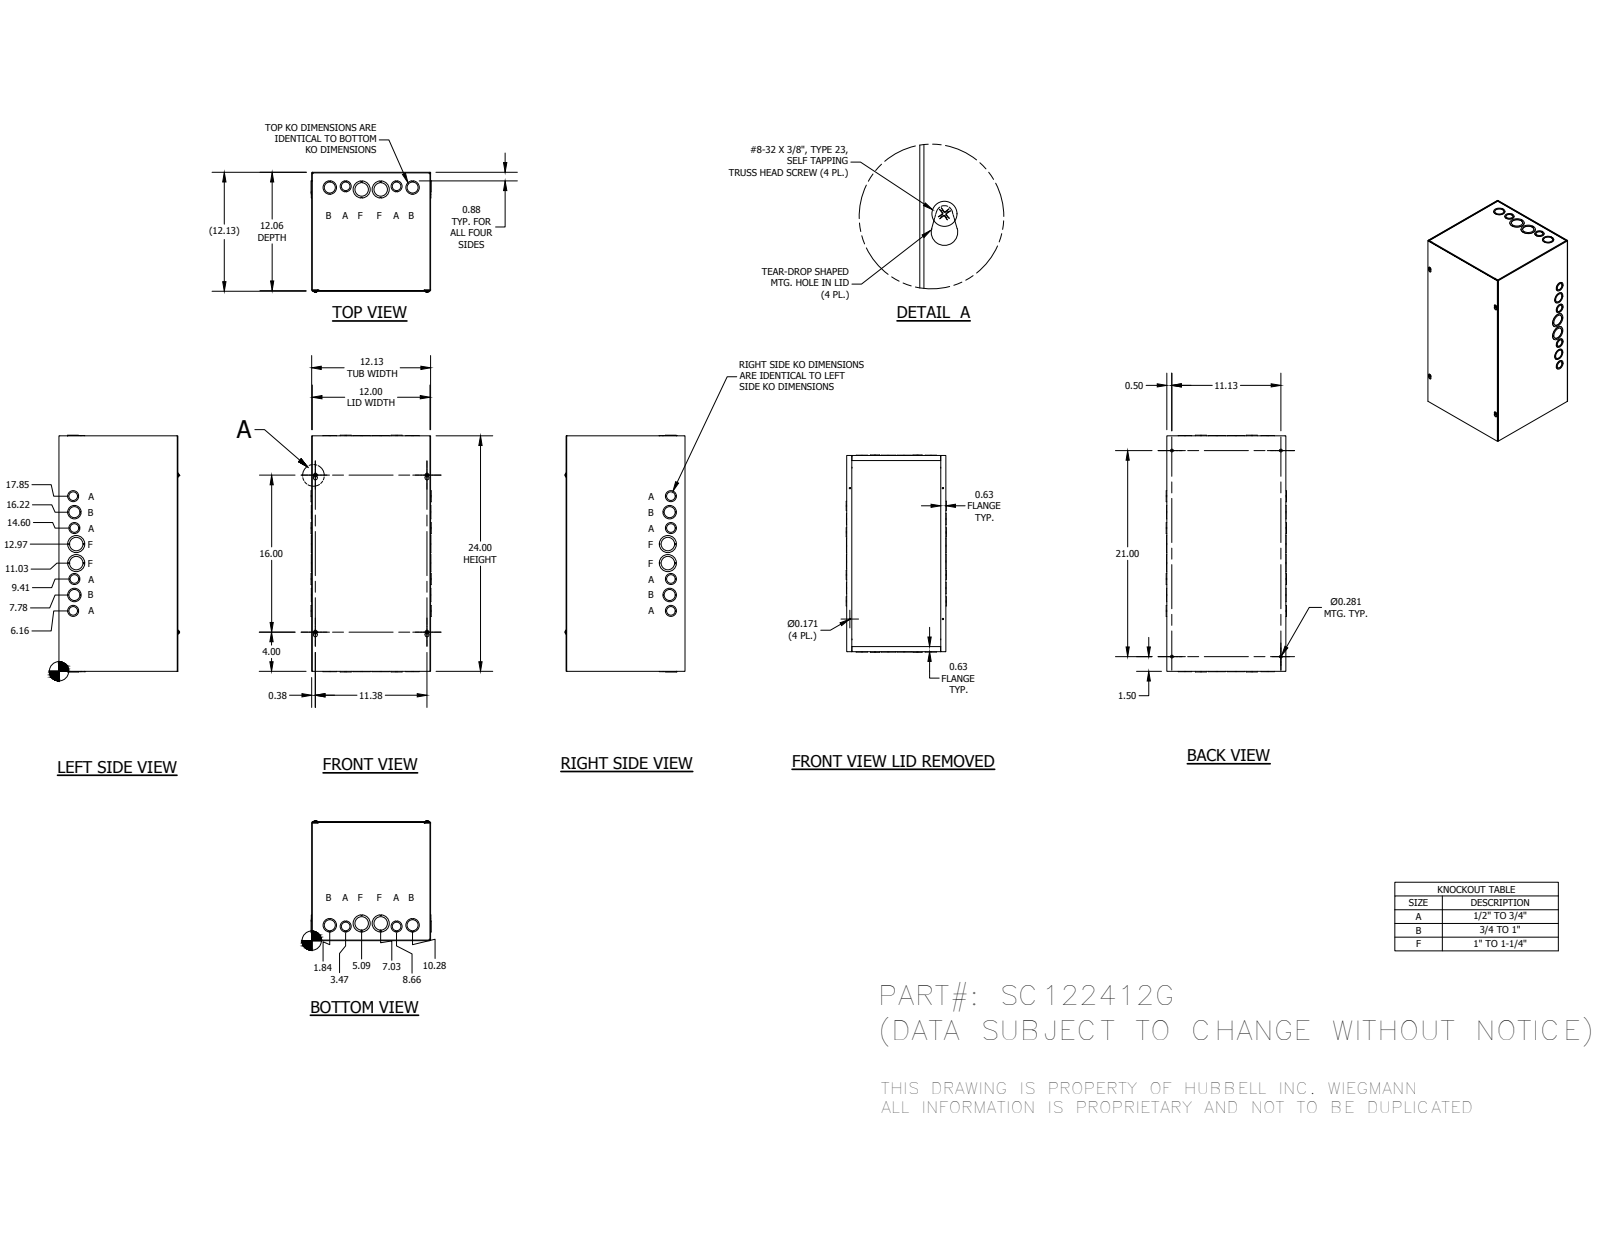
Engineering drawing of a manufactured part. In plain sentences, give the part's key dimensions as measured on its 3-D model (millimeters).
The part is named "SC122412GBLR; SC1212GTB; SC1224GLPA; 34056 (+1 more)". Its 3-D file was written by "Autodesk Inventor 2014 (AUTOMOTIVE_DESIGN)". It is 29 solids with 1055 faces: 771 planar, 216 cylindrical and 68 other. Overall it measures 612.77 by 311.15 by 310.52 millimeters. Round holes: 12 of diameter 28.57, 8 of diameter 22.22, 8 of diameter 34.92, 4 of diameter 4.34, 4 of diameter 7.14, 4 of diameter 44.45. Round bosses or shafts: 4 of diameter 9.75, 4 of diameter 4.17. Partial cylindrical surfaces (rounded edges, fillets, slot ends): 12 of radius 0.4, 12 of radius 1.98, 4 of radius 3.17, 4 of radius 5.16. The main face-to-face distances are 1.59, 306.39, 304.8, 307.98, 608.01, 609.6, 606.42, 3.18, 303.21, 0.79. The hole center spacings are 41.4, 42.03, 63.58, 82.69, 90.9, 131.92, 173.13, 292.72.
